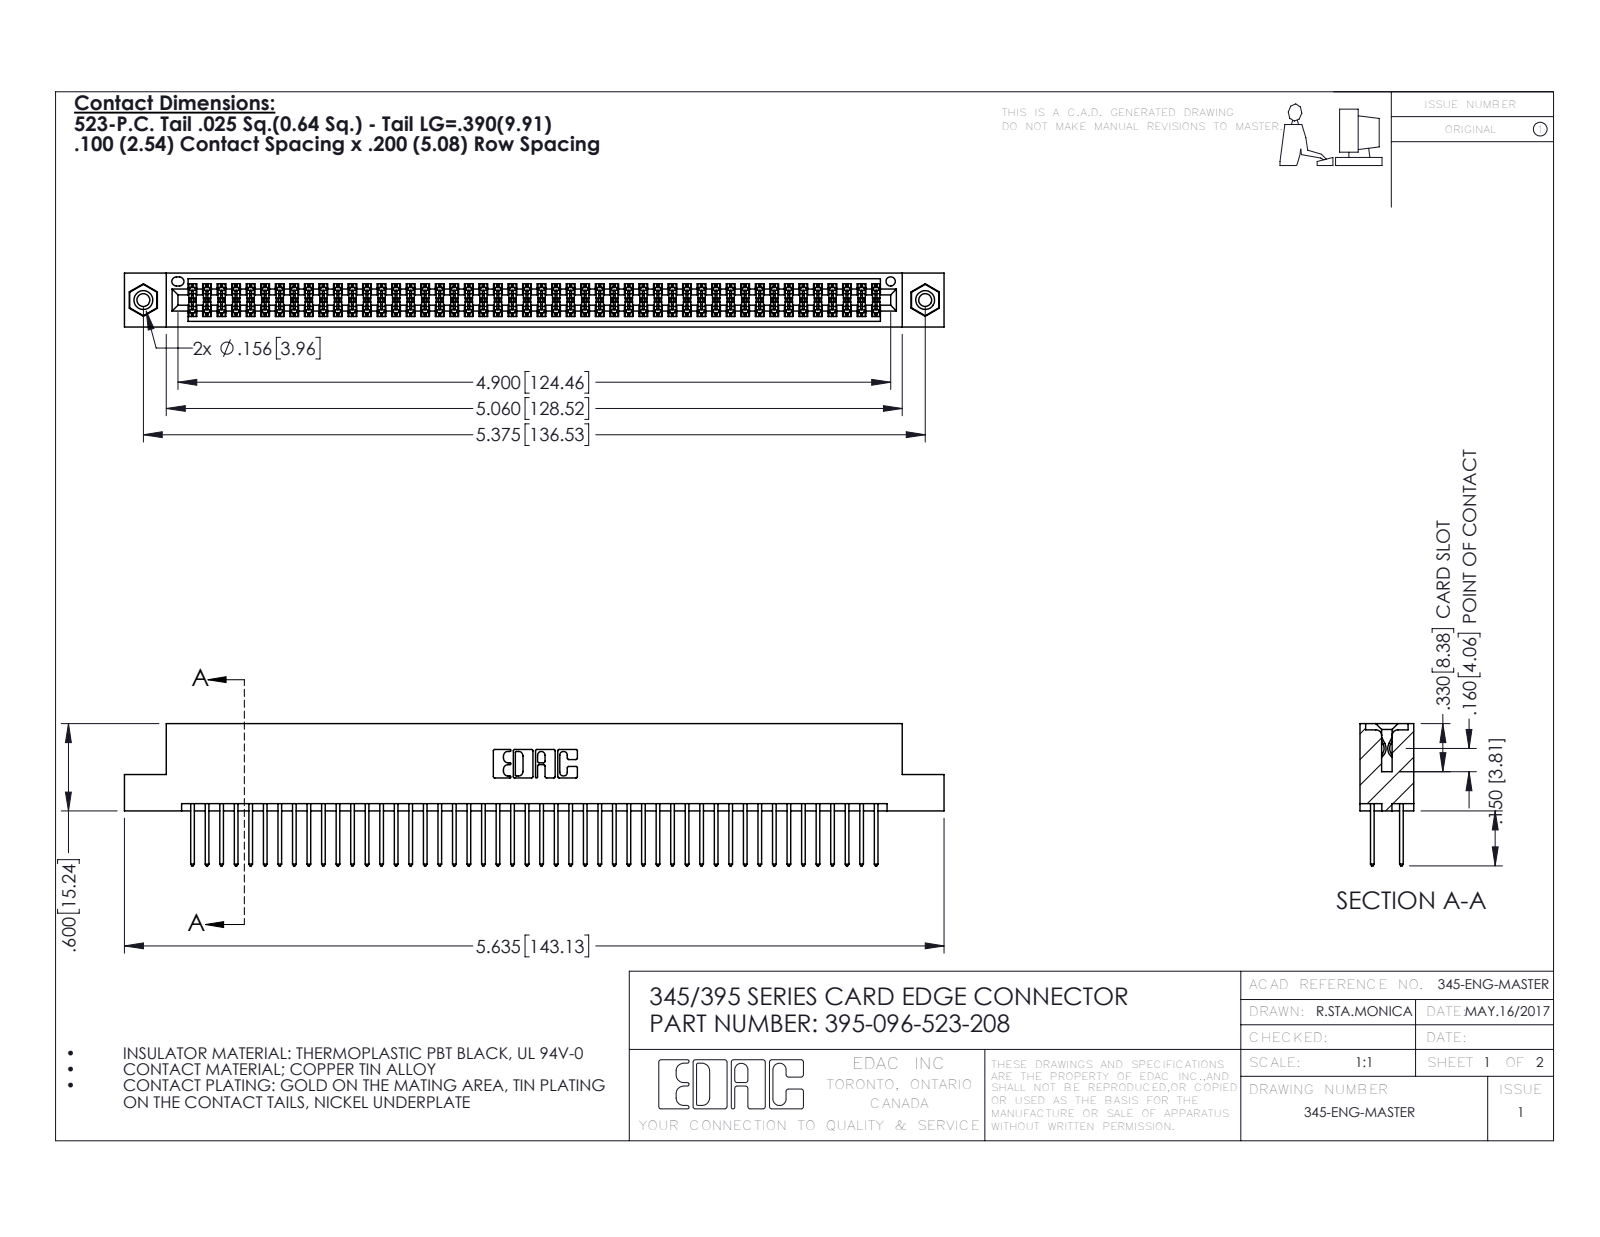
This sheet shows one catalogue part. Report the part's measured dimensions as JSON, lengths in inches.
{"part_name": "345-250-001_345-250-003-102; 345 Part_Flush Mounting Lugs - 0.156 Dia-TI; 395-096-523-208; 345-292-001_345-293-123", "step_written_by": "SolidWorks 2016 (CONFIG_CONTROL_DESIGN)", "units": "inches", "bodies": {"solids": 99, "faces": 4986, "planar": 3280, "cylindrical": 1690, "other": 16}, "overall_size": [5.635, 0.977, 0.37], "volume_in3": 0.863, "surface_area_in2": 33.99, "round_holes": [[0.089, 2], [0.125, 2], [0.156, 2], [0.064, 1]], "round_bosses_or_shafts": [[0.155, 2]], "partial_cylinders_radius": [[0.006, 144], [0.01, 96], [0.01, 22], [0.007, 6], [0.031, 6], [0.026, 3], [0.014, 2], [0.019, 2]], "face_to_face_distances": [0.072, 0.298, 0.2, 0.098, 0.272, 0.025, 0.37, 0.225, 0.175, 0.149], "hole_center_spacings": [0.27, 5.139, 5.375]}
